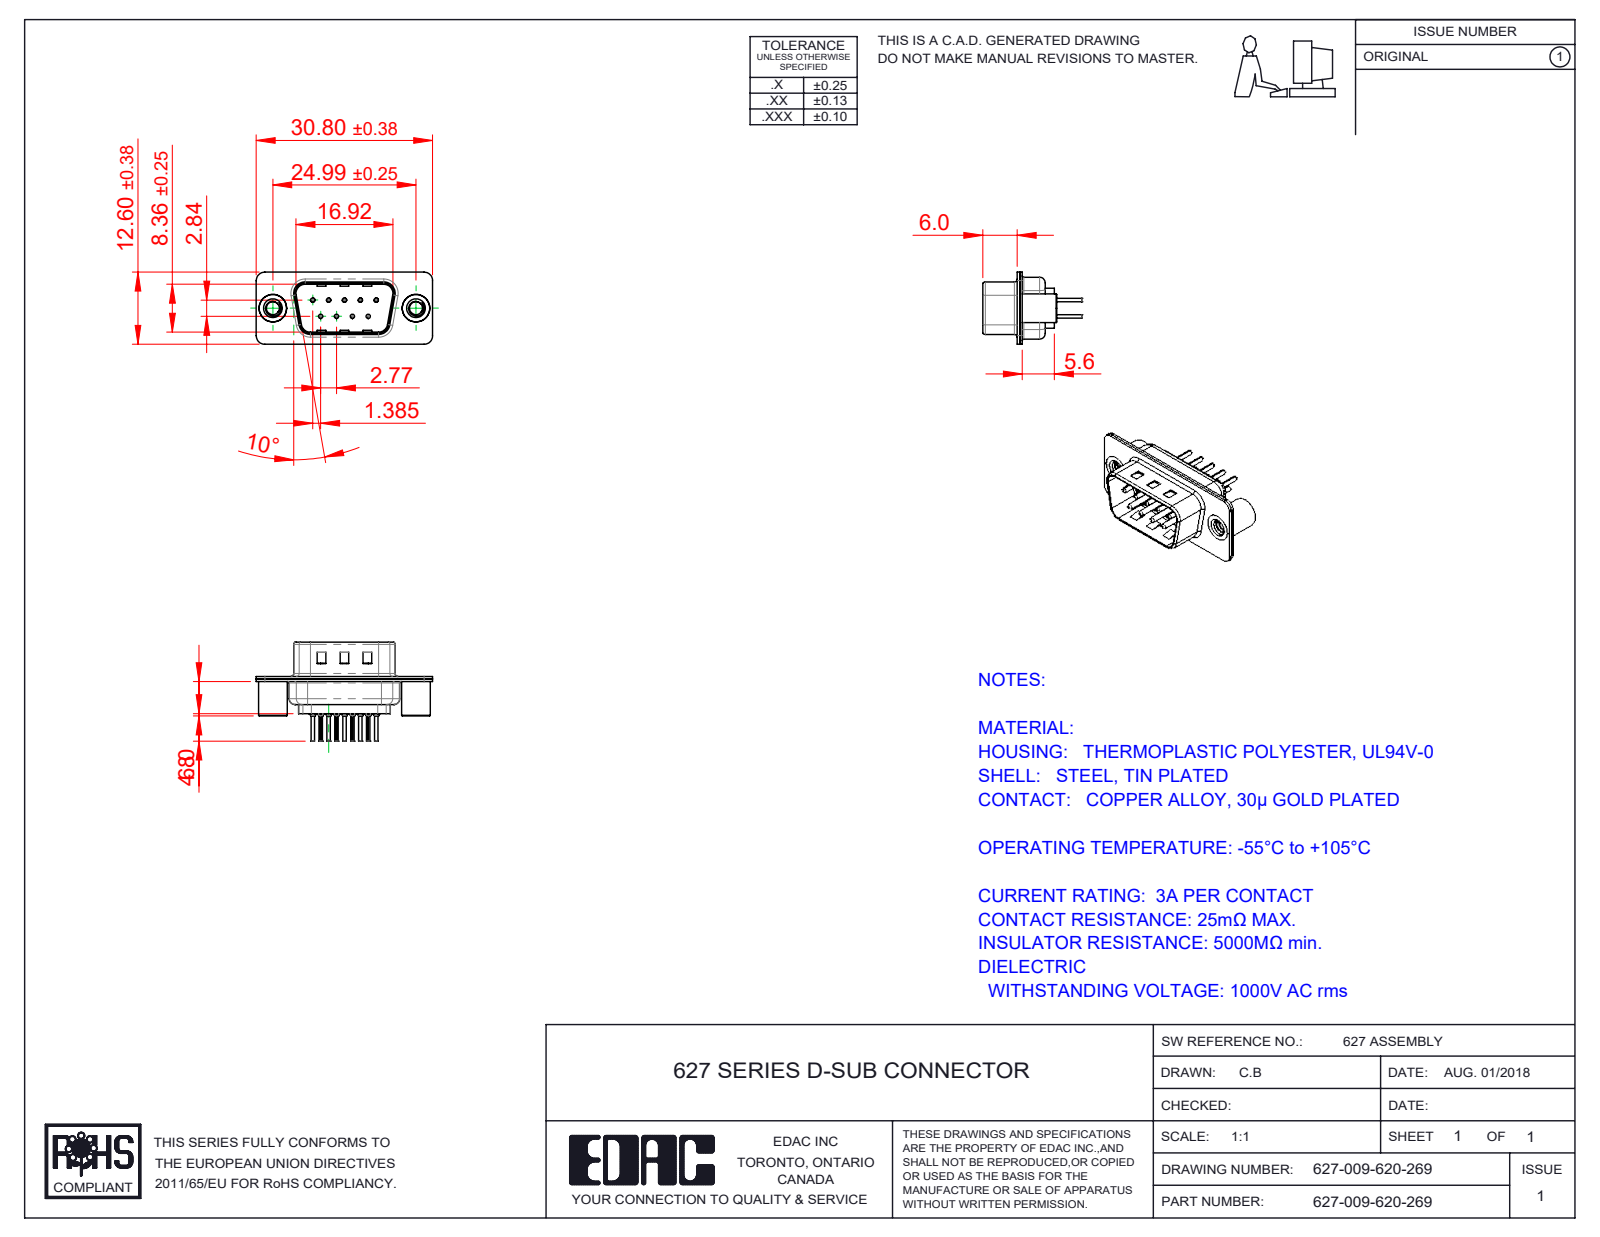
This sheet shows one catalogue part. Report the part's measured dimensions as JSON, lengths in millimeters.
{"part_name": "627 4-40 Threaded Standoff BS; 627 Housing_09 LP; 627-009-620-069; 627 Shell Rear_09 Contacts (+3 more)", "step_written_by": "SolidWorks 2020 (CONFIG_CONTROL_DESIGN)", "units": "millimeters", "bodies": {"solids": 14, "faces": 1208, "planar": 323, "cylindrical": 482, "other": 403}, "overall_size": [30.8, 17.3, 12.6], "volume_mm3": 1408, "surface_area_mm2": 4125, "round_holes": [[0.2, 9], [0.35, 9], [1.1, 9], [1.6, 9], [2.26, 2], [4, 2], [4.8, 2]], "round_bosses_or_shafts": [[2, 9], [1.5, 9], [0.75, 9], [0.6, 9], [5, 2], [4.9, 2]], "partial_cylinders_radius": [[0.1, 18], [1.5, 18], [2, 12], [0.5, 8], [1.6, 8], [0.25, 4], [0.6, 4], [0.65, 4]], "face_to_face_distances": [0.45, 0.4, 0.9, 0.82, 9.58, 1.4, 8.76, 6.5, 0.5, 1.5], "hole_center_spacings": [3.16, 2.77, 5.54, 5.03, 5.04, 8.31, 7.48, 7.49]}
